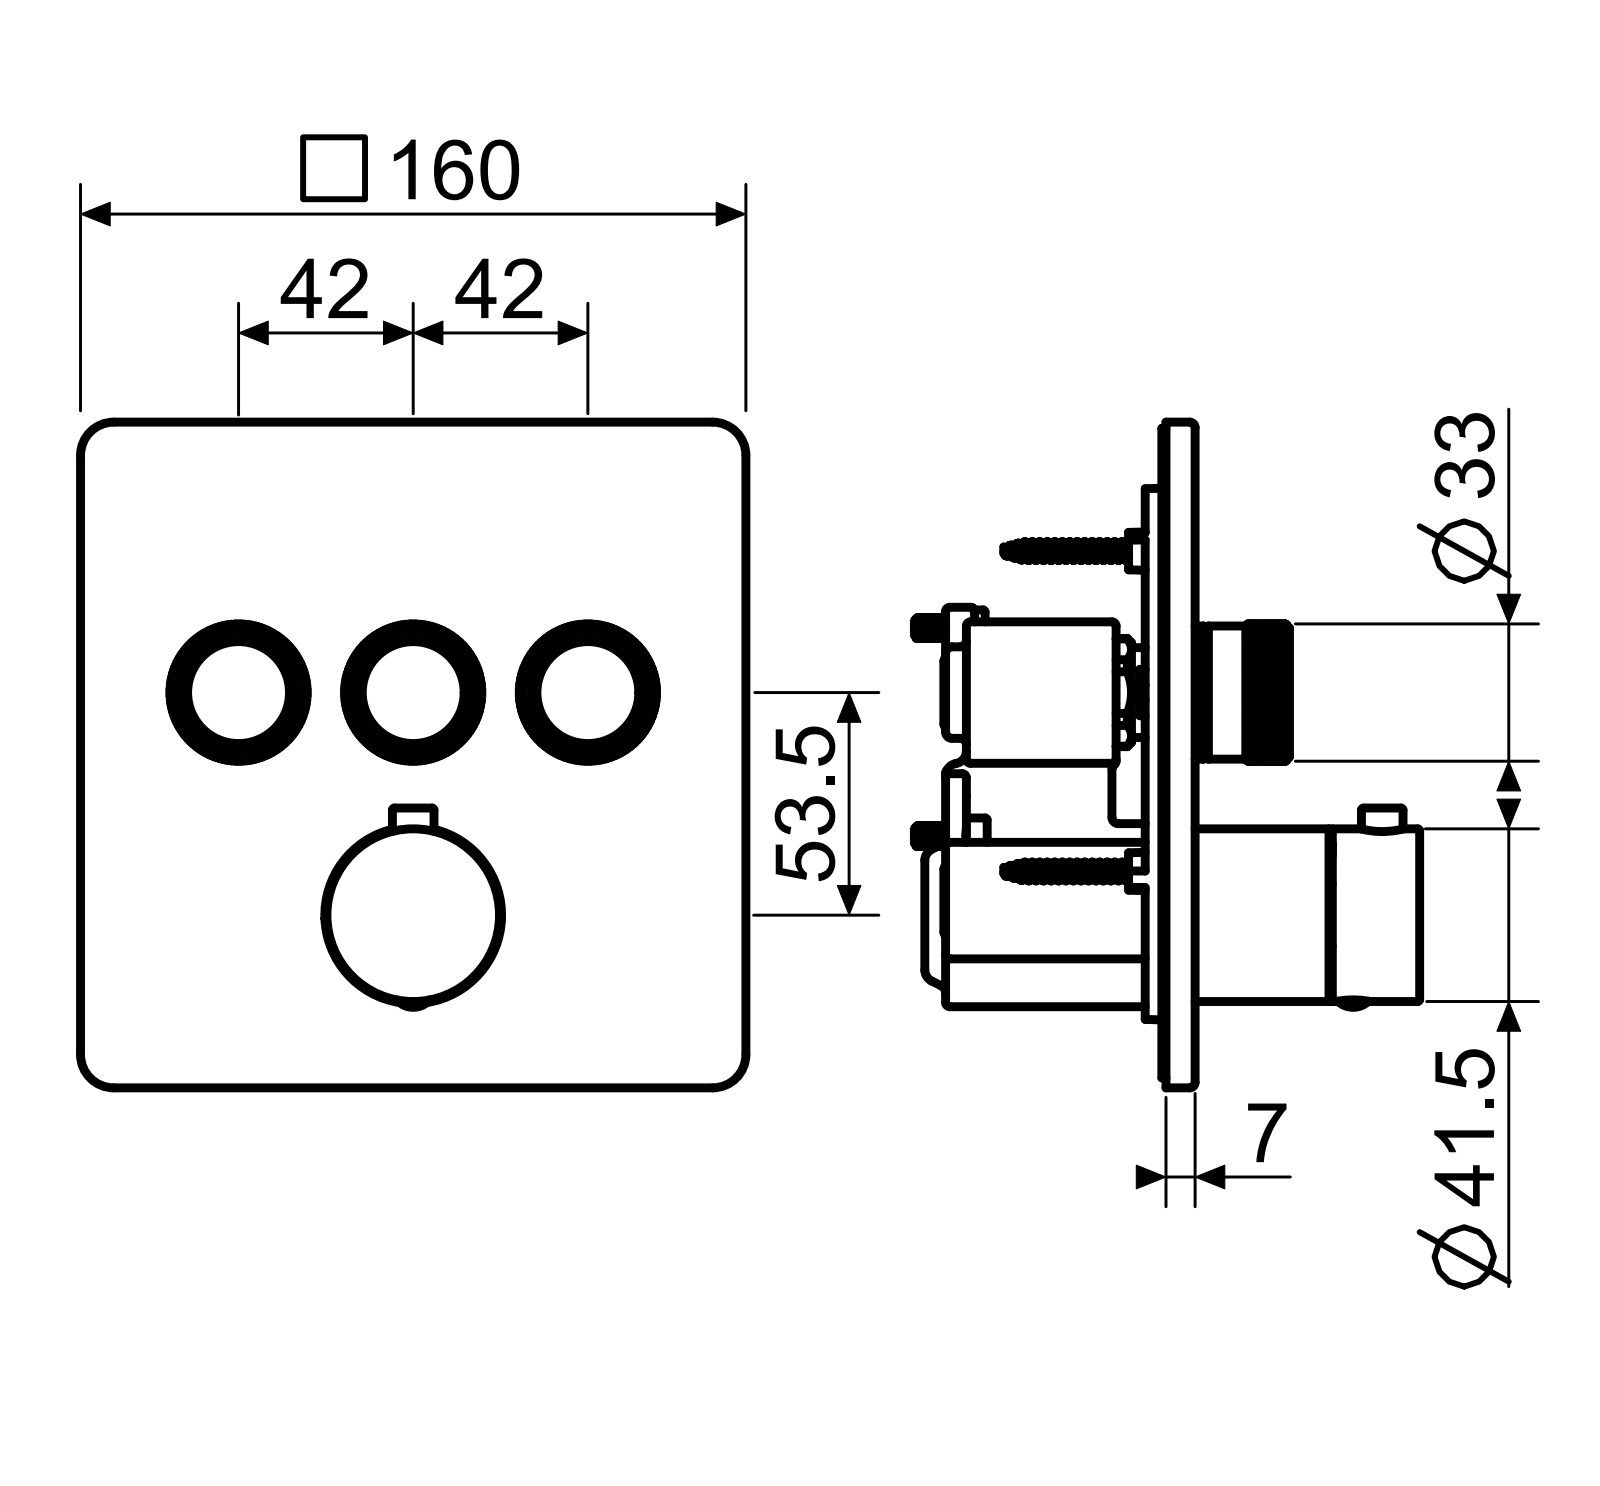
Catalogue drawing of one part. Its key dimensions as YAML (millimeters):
part_name: "SINMAC0010; AIMA693C016; AIMA005C001; SPLMAC0005 (+6 more)"
step_written_by: "CREO PARAMETRIC BY PTC INC, 2022164 (CONFIG_CONTROL_DESIGN)"
units: millimeters
bodies: {solids: 17, faces: 13729, planar: 4101, cylindrical: 4276, other: 5352}
overall_size: [160, 160, 66.87]
volume: 78909
surface_area: 112169
round_holes:
  - {diameter: 20, count: 3}
  - {diameter: 20.5, count: 3}
  - {diameter: 21.5, count: 3}
  - {diameter: 22, count: 3}
  - {diameter: 22.5, count: 3}
  - {diameter: 23, count: 3}
  - {diameter: 26, count: 3}
  - {diameter: 26.9, count: 3}
  - {diameter: 27, count: 3}
  - {diameter: 28, count: 3}
  - {diameter: 30, count: 3}
  - {diameter: 30.5, count: 3}
round_bosses_or_shafts:
  - {diameter: 32, count: 3}
  - {diameter: 29.9, count: 3}
  - {diameter: 29.8, count: 3}
  - {diameter: 26.8, count: 3}
  - {diameter: 25.5, count: 3}
  - {diameter: 23.7, count: 3}
  - {diameter: 41.5, count: 1}
  - {diameter: 15, count: 1}
partial_cylinders:
  - {radius: 0.1, count: 256}
  - {radius: 2, count: 36}
  - {radius: 0.15, count: 24}
  - {radius: 1.25, count: 24}
  - {radius: 3, count: 18}
  - {radius: 0.5, count: 4}
  - {radius: 1.3, count: 4}
  - {radius: 7.2, count: 4}
face_to_face_distances: [0.8, 159.2, 23.9, 23.1, 158.4, 160, 1.5, 22.4, 3.1, 21.6]
hole_center_spacings: [42, 56.47, 68.02, 7, 15.75, 37.75, 53.5, 84]
